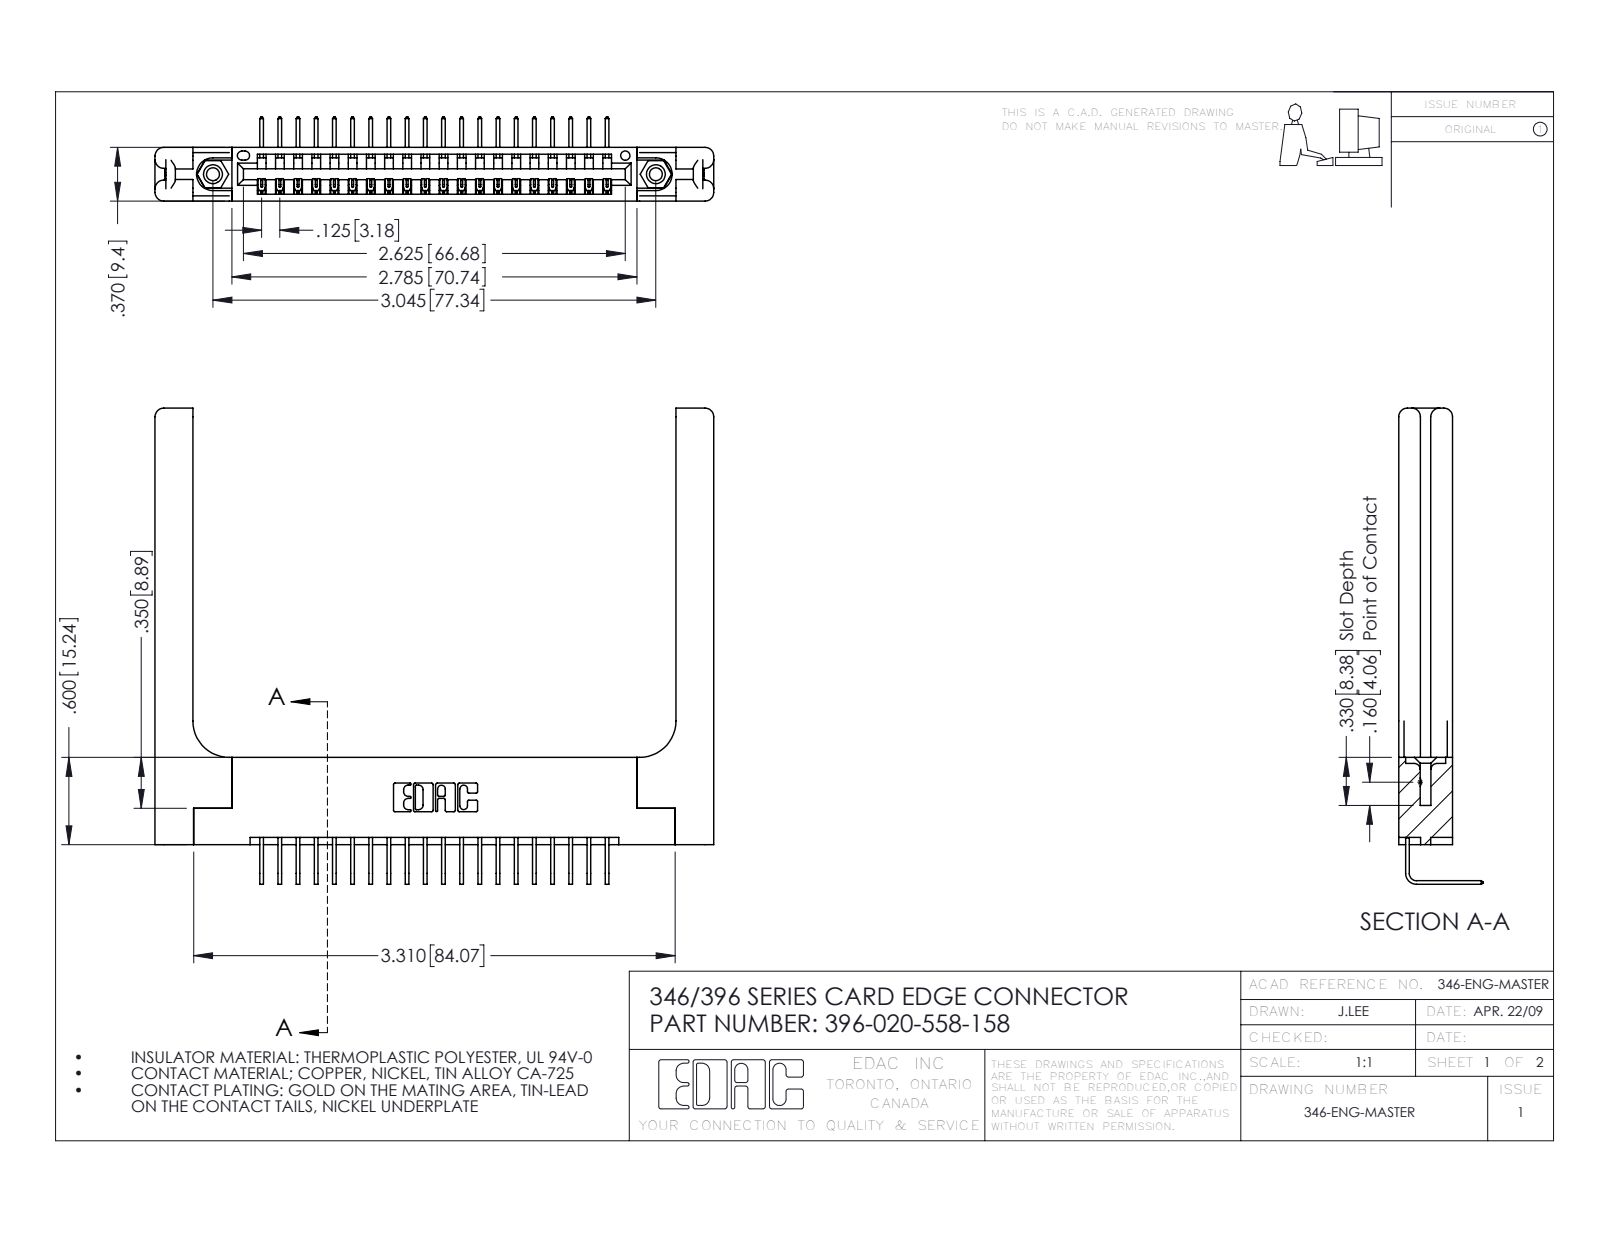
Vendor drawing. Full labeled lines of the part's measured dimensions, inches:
Part name (STEP PRODUCT): 396-020-558-158; 346-220-058_345-220-058; 345-292-001_558 Tail - 2; 345-250-001_345-250-001-102 (+1 more)
STEP written by: SolidWorks 2016 (CONFIG_CONTROL_DESIGN)
Units: inches
Bodies: 25 solids, 1578 faces (1064 planar, 454 cylindrical, 60 other)
Overall size (bounding box): 3.841 × 3.273 × 0.58
Volume: 1.024 in³ · Surface area: 26.19 in²
Round holes (diameter × count): ⌀0.089 ×2, ⌀0.125 ×2, ⌀0.156 ×2, ⌀0.064 ×1
Round bosses / shafts (diameter × count): ⌀0.155 ×2
Partial cylindrical surfaces — rounded edges, fillets, slot ends (radius × count): R0.006 ×40, R0.01 ×22, R0.06 ×16, R0.007 ×6, R0.031 ×6, R0.026 ×3, R0.03 ×2, R0.031 ×2
Main face-to-face distances: 0.37, 0.072, 0.322, 0.15, 0.148, 0.048, 0.25, 0.025, 0.298, 0.102
Hole centre spacings: 0.246, 2.837, 3.045
